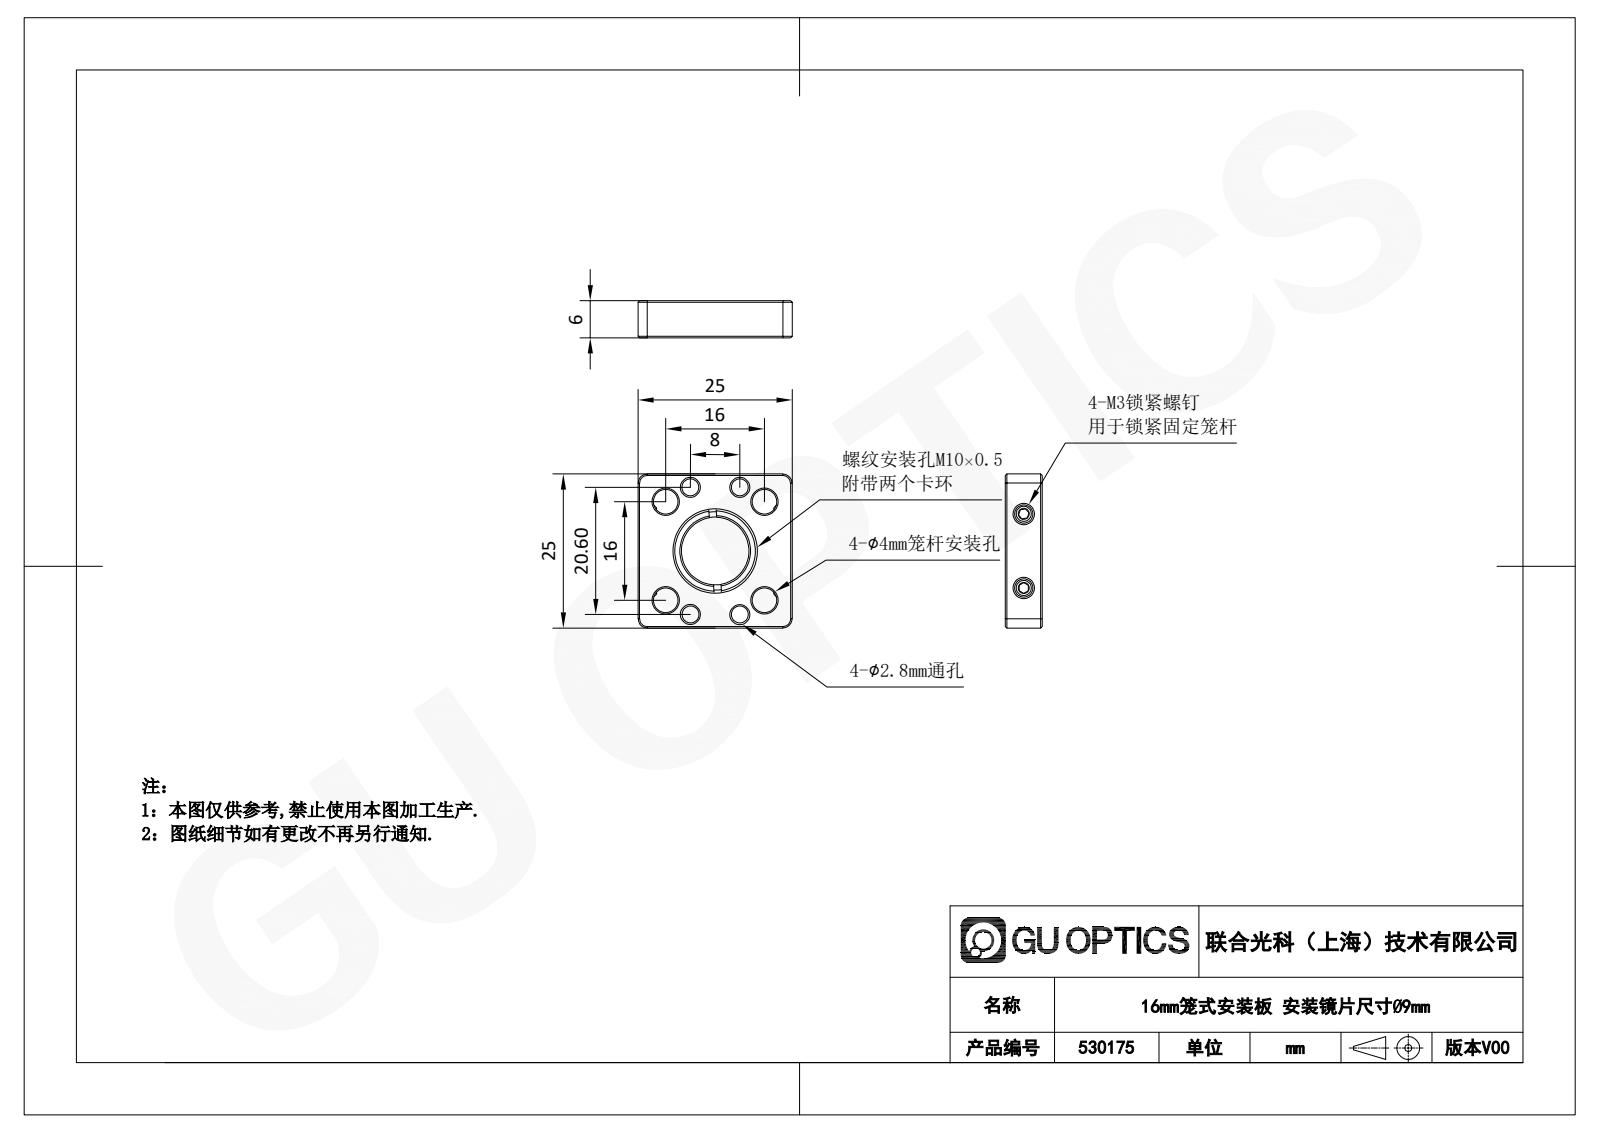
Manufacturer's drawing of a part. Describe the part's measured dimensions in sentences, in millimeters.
The part is named "530175". Its 3-D file was written by "SolidWorks 2020 (CONFIG_CONTROL_DESIGN)". It is 7 solids with 284 faces: 135 planar, 25 cylindrical and 124 other. Overall it measures 25 by 25 by 6 millimeters. Its volume is 2 975 cubic millimeters and its surface area 2 762 square millimeters. Round holes: 4 of diameter 2.8, 4 of diameter 4, 2 of diameter 2.5, 1 of diameter 7, 1 of diameter 9.5. Round bosses or shafts: 2 of diameter 3, 1 of diameter 10. Partial cylindrical surfaces (rounded edges, fillets, slot ends): 4 of radius 1.5. The main face-to-face distances are 6, 25, 2, 4, 21.56, 3, 22, 1.5, 1, 24. The hole center spacings are 4.61, 11.05, 11.31, 12.22, 16, 18.73, 21.88, 8.
